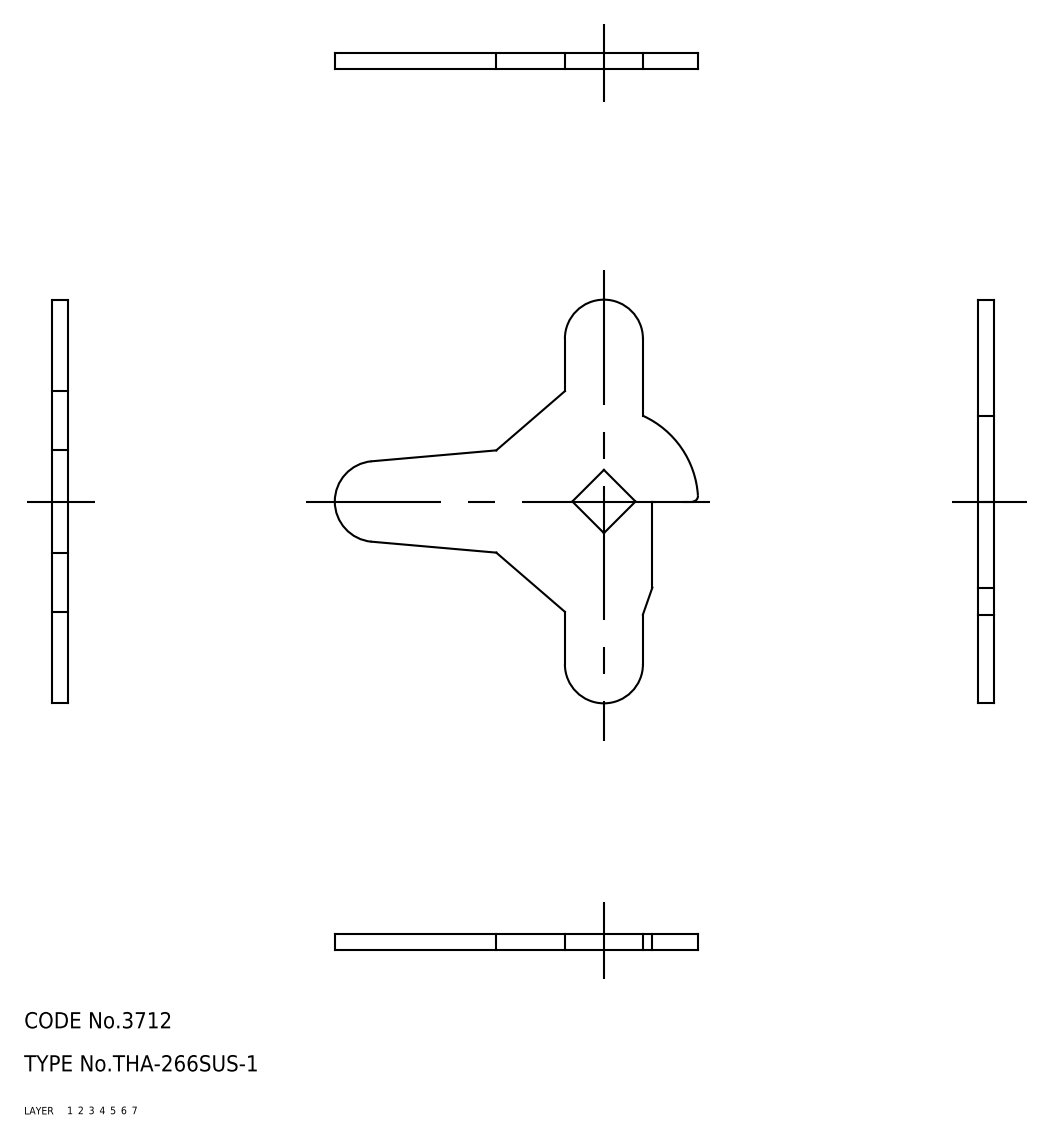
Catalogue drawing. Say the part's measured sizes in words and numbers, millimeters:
The part is named "cam". Its 3-D file was written by "CADfix (AUTOMOTIVE_DESIGN)". It is 1 solid with 21 faces: 0 planar, 0 cylindrical and 21 other. Overall it measures 75 by 67.5 by 3 millimeters. Its volume is 5 932 cubic millimeters and its surface area 4 777 square millimeters.
